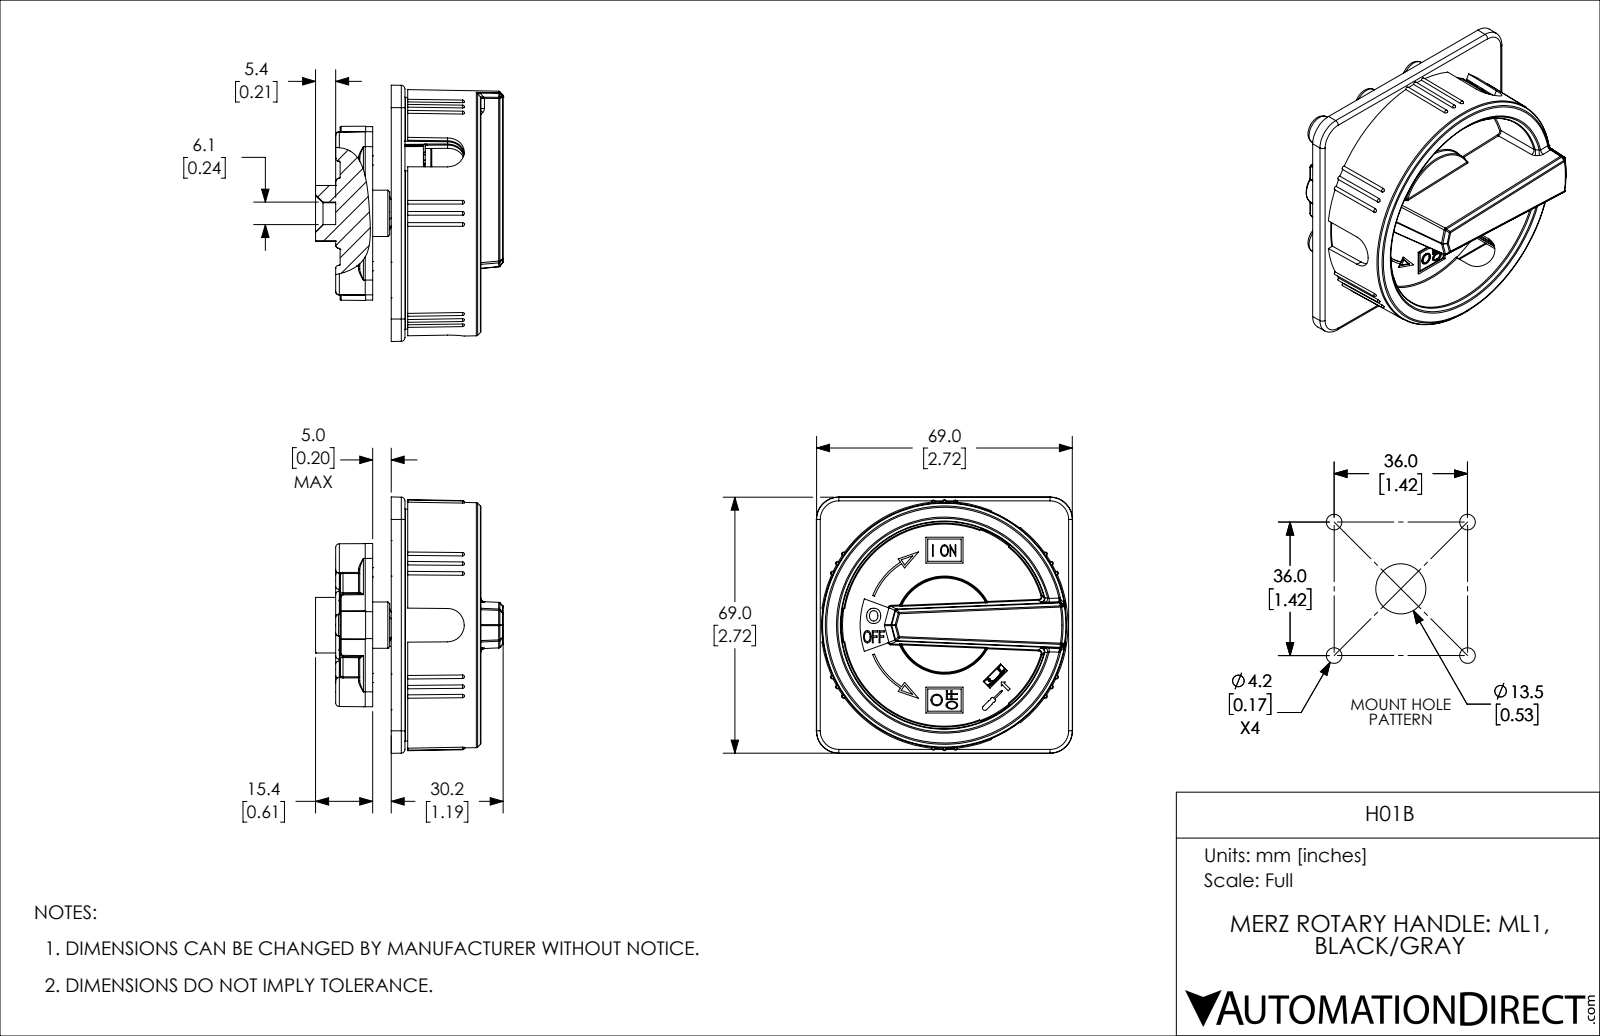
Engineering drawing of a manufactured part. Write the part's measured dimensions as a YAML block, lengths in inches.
part_name: "H01B"
step_written_by: "SolidWorks 2019 (AUTOMOTIVE_DESIGN)"
units: inches
bodies: {solids: 1, faces: 2282, planar: 467, cylindrical: 403, other: 1412}
overall_size: [2.722, 2.722, 1.992]
volume: 2.958
surface_area: 75.29
round_bosses_or_shafts:
  - {diameter: 0.197, count: 6}
  - {diameter: 1.024, count: 1}
  - {diameter: 0.591, count: 1}
  - {diameter: 0.492, count: 1}
  - {diameter: 0.236, count: 1}
partial_cylinders:
  - {radius: 0.02, count: 114}
  - {radius: 0.012, count: 48}
  - {radius: 0.039, count: 26}
  - {radius: 0.031, count: 22}
  - {radius: 0.01, count: 15}
  - {radius: 0.008, count: 6}
  - {radius: 0.035, count: 6}
  - {radius: 0.055, count: 5}
face_to_face_distances: [0.059, 0.197, 0.02, 0.079, 0.276, 0.138, 0.217, 0.559, 0.362, 0.343]
